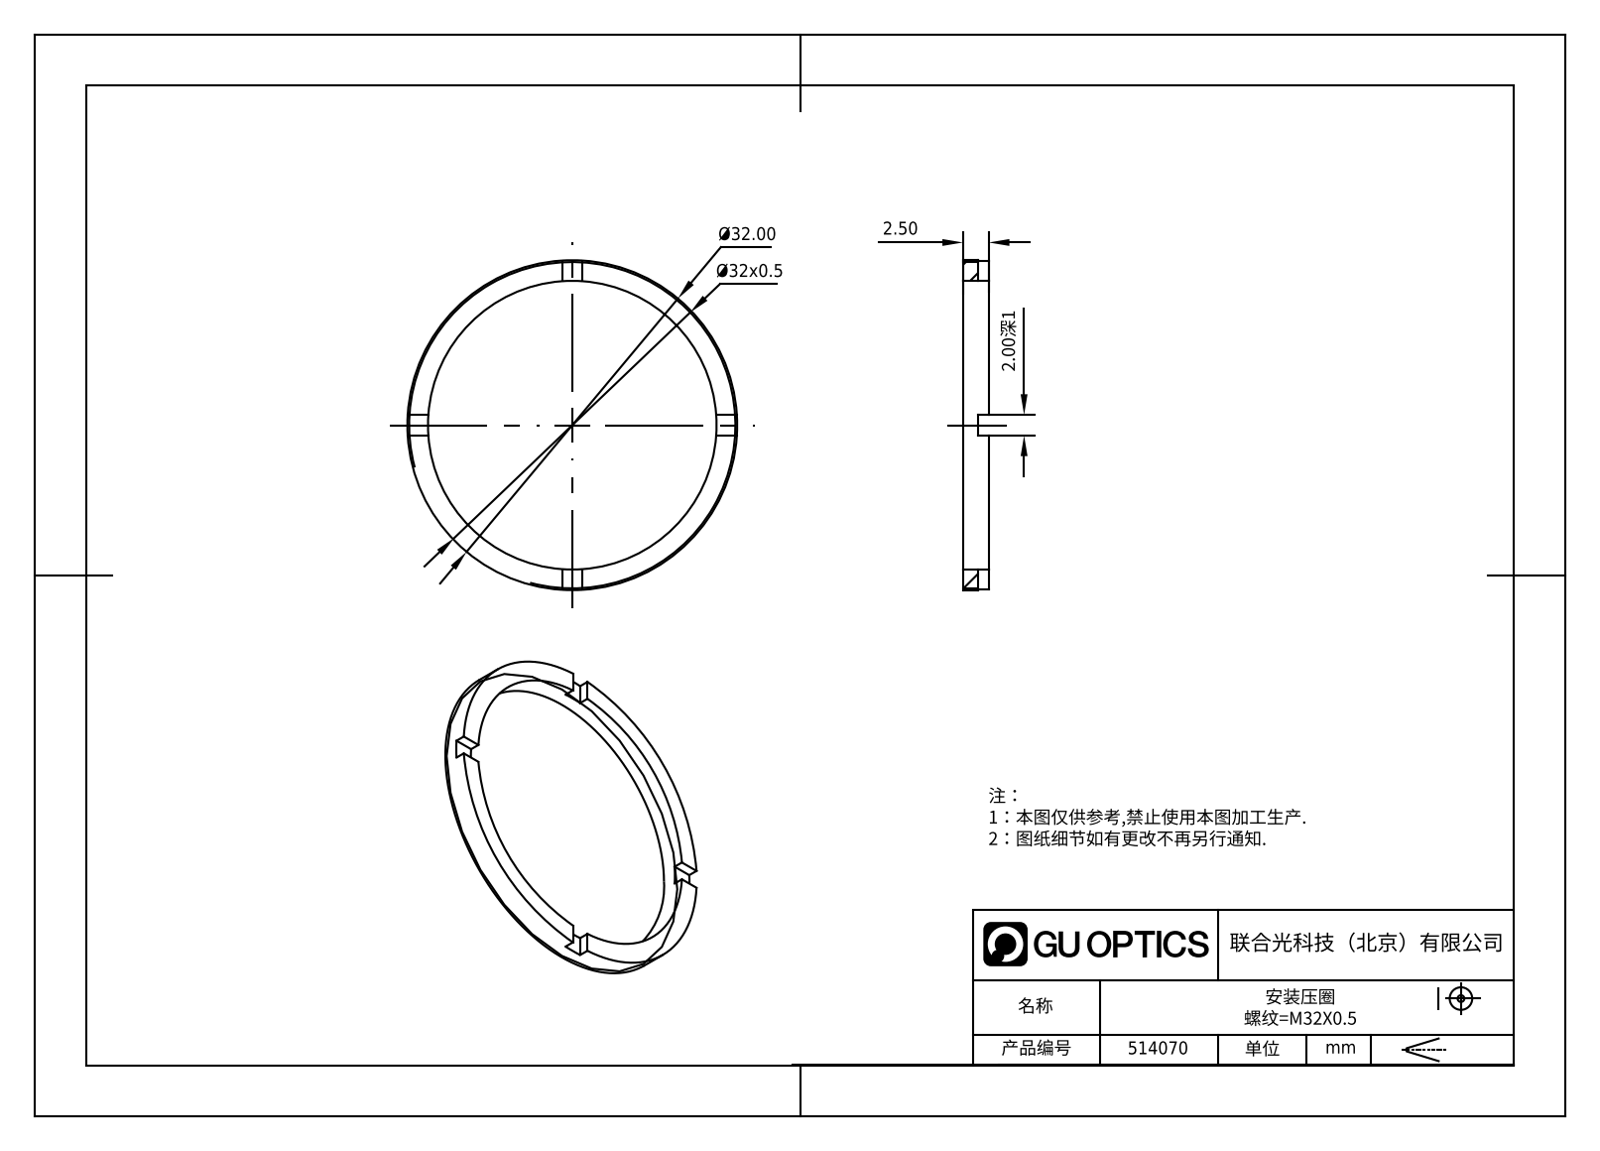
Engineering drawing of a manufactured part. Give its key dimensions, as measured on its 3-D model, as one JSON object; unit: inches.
{"part_name": "514070", "step_written_by": "SolidWorks 2020 (CONFIG_CONTROL_DESIGN)", "units": "inches", "bodies": {"solids": 1, "faces": 21, "planar": 17, "cylindrical": 4, "other": 0}, "overall_size": [1.26, 1.26, 0.098], "volume_in3": 0.028, "surface_area_in2": 1.31, "round_holes": [[1.102, 1]], "round_bosses_or_shafts": [[1.26, 1]], "face_to_face_distances": [0.098, 0.059, 0.039, 0.079]}
